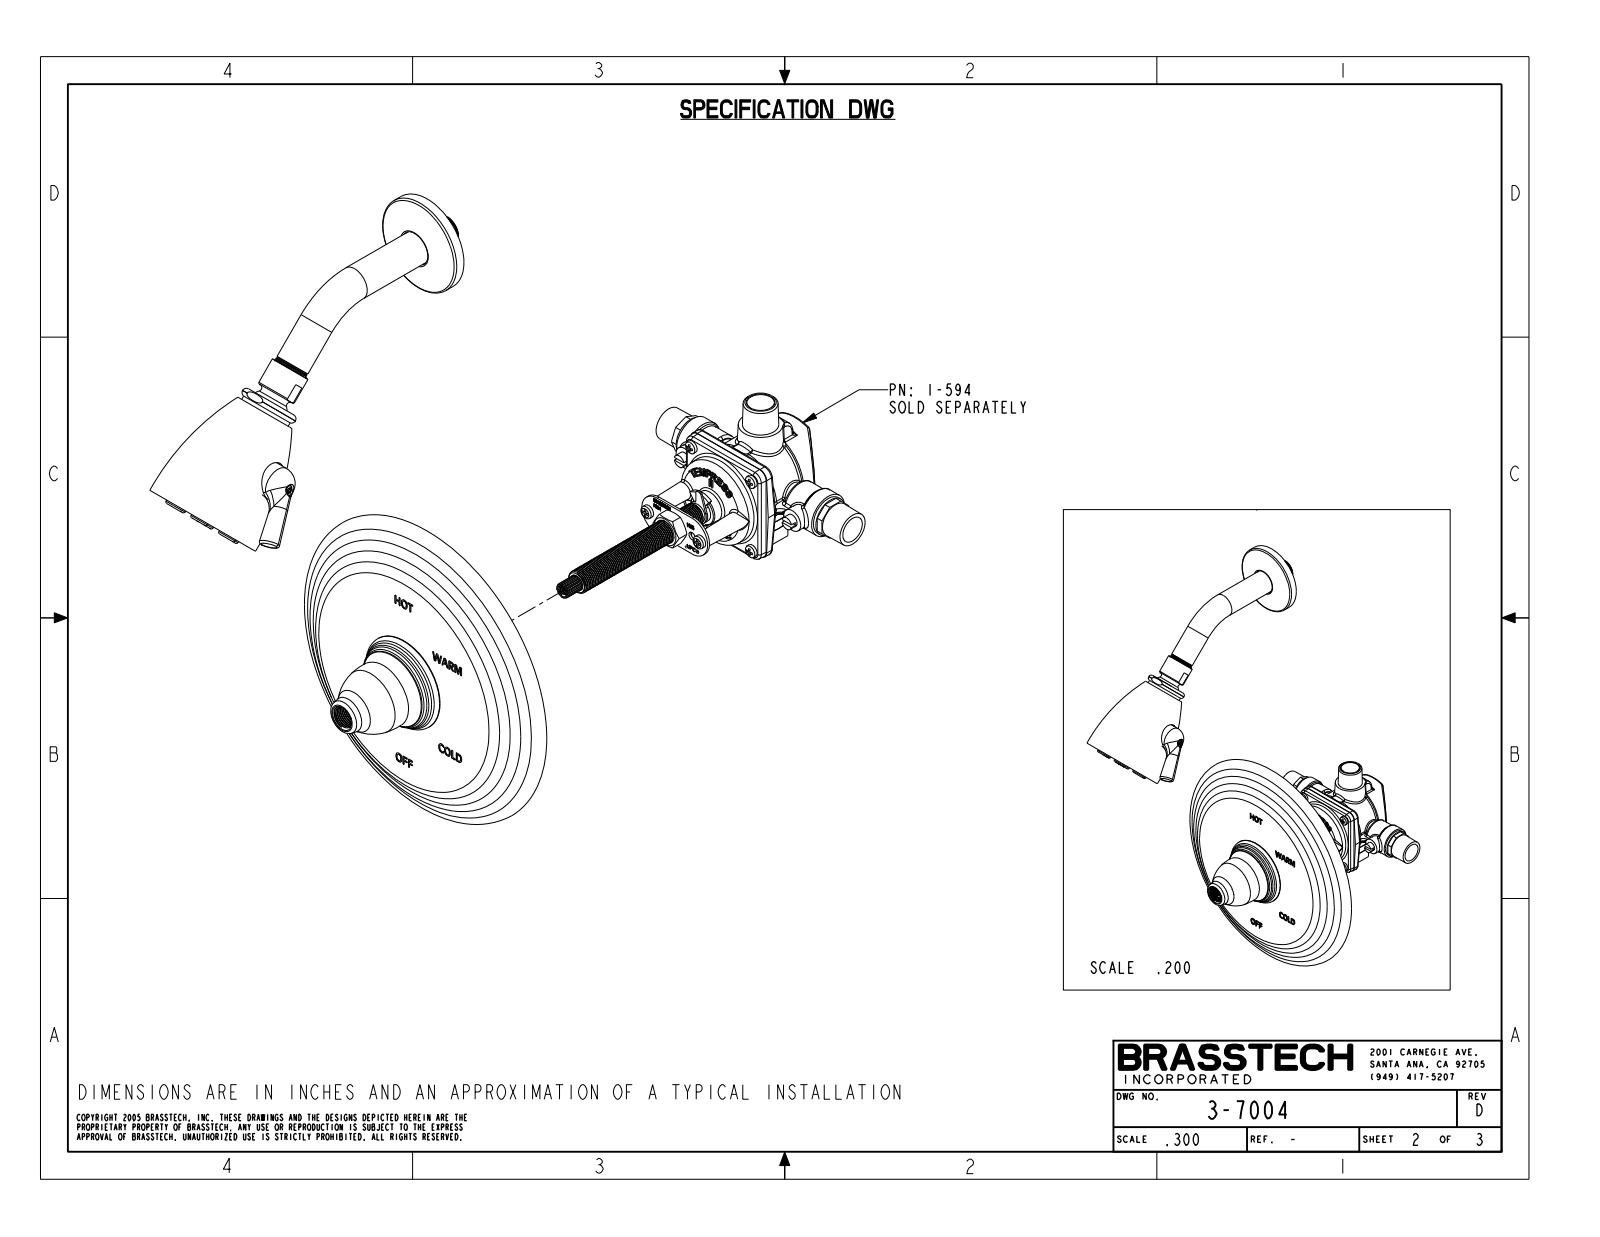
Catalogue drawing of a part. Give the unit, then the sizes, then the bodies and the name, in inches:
Units: inches
Overall size (bounding box): 17.065 × 8.403 × 7.75
Round holes (diameter × count): ⌀0.684 ×2, ⌀0.187 ×1, ⌀0.235 ×1, ⌀0.43 ×1, ⌀0.508 ×1, ⌀0.563 ×1, ⌀0.648 ×1, ⌀0.715 ×1, ⌀2.125 ×1, ⌀2.34 ×1
Round bosses / shafts (diameter × count): ⌀0.1 ×6, ⌀0.813 ×2, ⌀2.38 ×1, ⌀2.34 ×1, ⌀1.219 ×1, ⌀0.892 ×1, ⌀0.8 ×1, ⌀0.768 ×1
Partial cylindrical surfaces — rounded edges, fillets, slot ends (radius × count): R0.007 ×12, R0.03 ×2, R0.114 ×1, R0.421 ×1, R0.468 ×1, R0.689 ×1
Main face-to-face distances: 0.05, 0.1, 0.704, 0.754, 2.107, 1.403, 1.353, 3.157, 3.057, 2.9
Hole centre spacings: 12
Bodies: 0 solids, 584 faces (214 planar, 195 cylindrical, 175 other)
Part name (STEP PRODUCT): 3-7004_SW0001
STEP written by: PRO/ENGINEER BY PARAMETRIC TECHNOLOGY CORPORATION, 2009300 (CONFIG_CONTROL_DESIGN)
